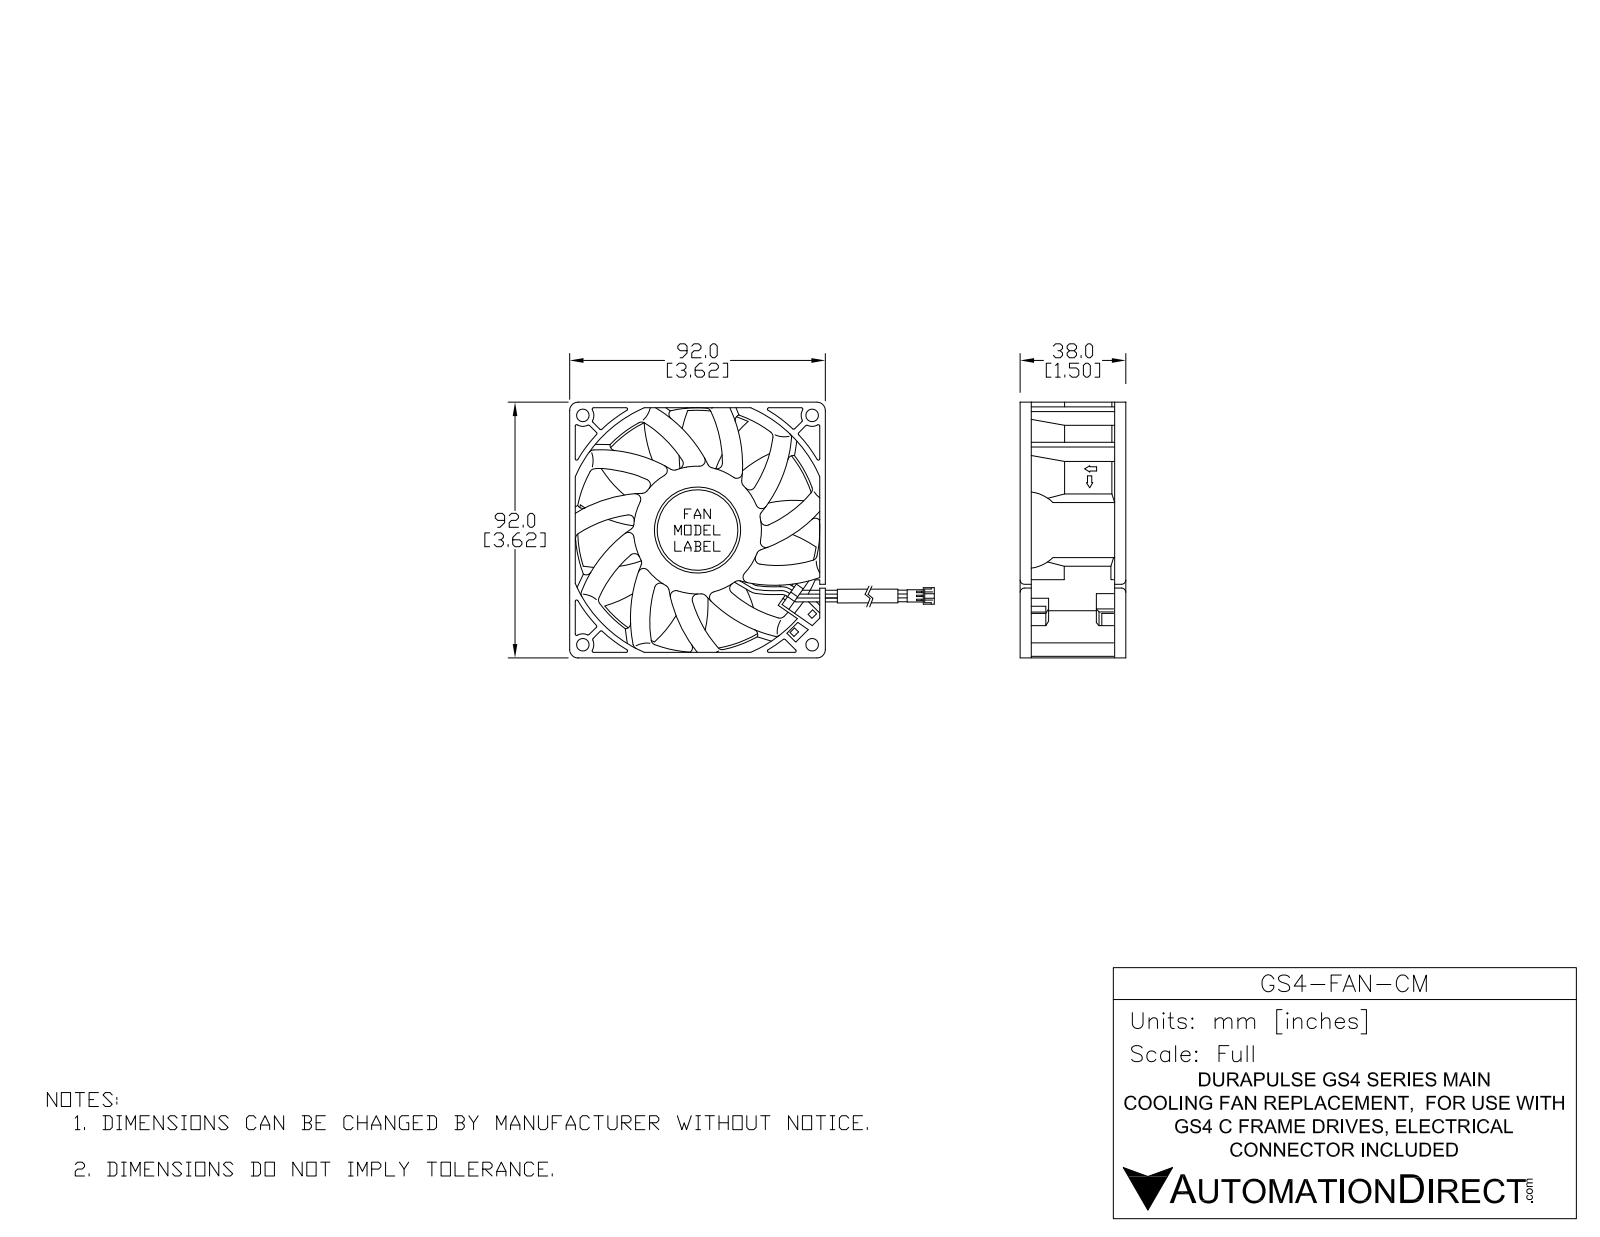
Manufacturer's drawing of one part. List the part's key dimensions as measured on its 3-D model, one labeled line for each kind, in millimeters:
Part name (STEP PRODUCT): GS4-FAN-CM
STEP written by: SolidWorks 2015 (AUTOMOTIVE_DESIGN)
Units: millimetres
Bodies: 0 solids, 60 faces (26 planar, 34 cylindrical, 0 other)
Overall size (bounding box): 92.5 × 92.5 × 38
Round bosses / shafts (diameter × count): ⌀4.5 ×4, ⌀37 ×1
Partial cylindrical surfaces — rounded edges, fillets, slot ends (radius × count): R2 ×4, R50 ×1, R51 ×1
Main face-to-face distances: 1, 89, 88, 90, 1.25, 2.25, 90.25, 91.25, 38, 4
